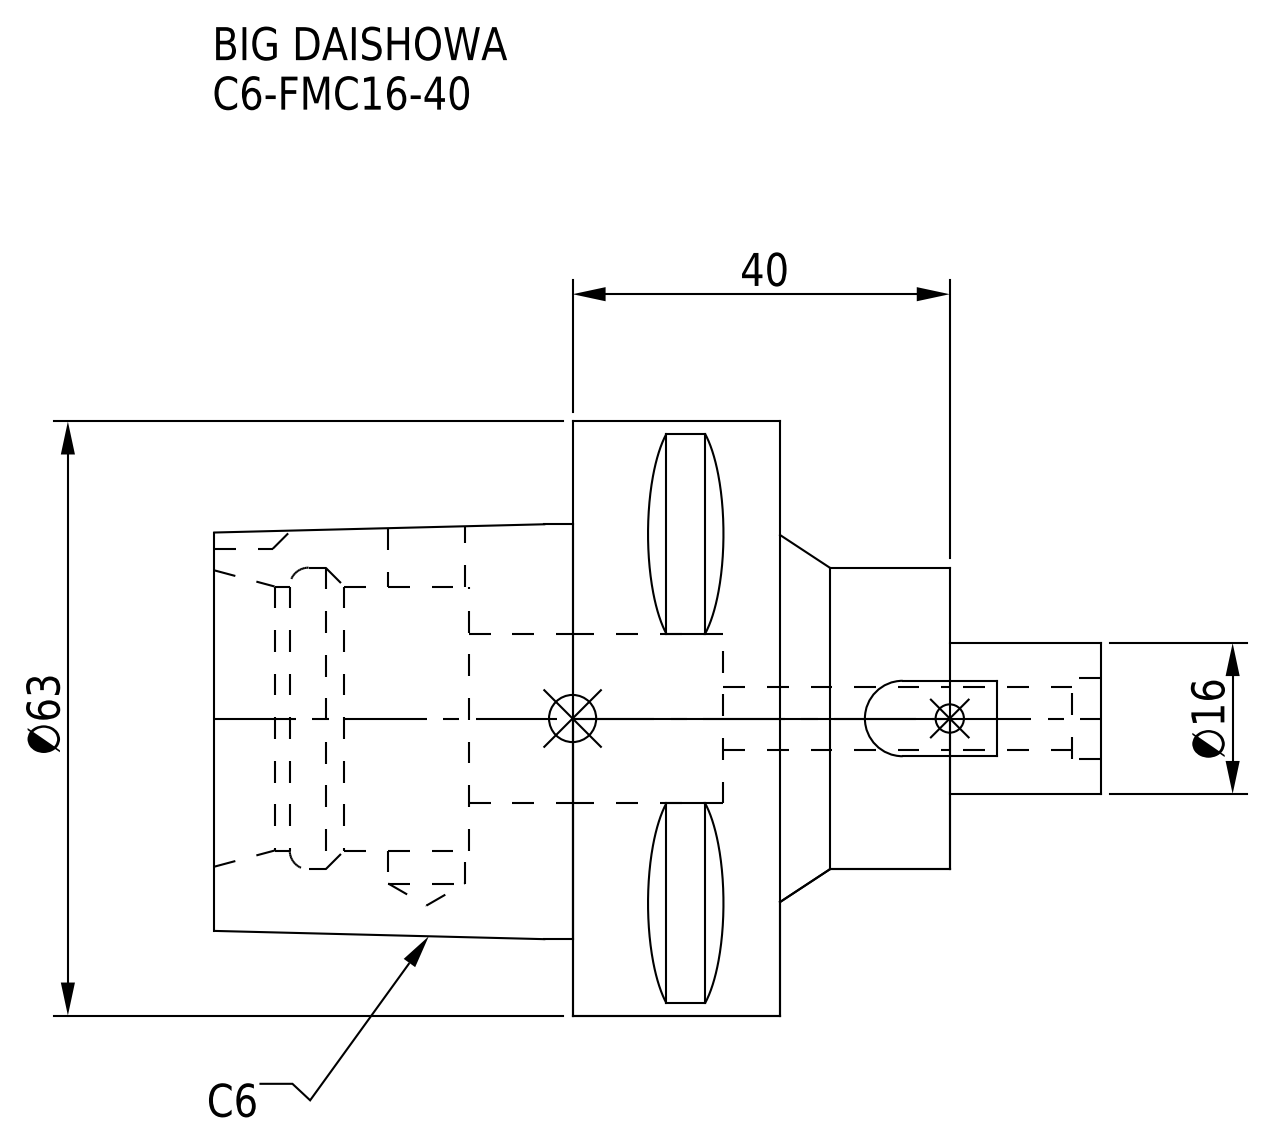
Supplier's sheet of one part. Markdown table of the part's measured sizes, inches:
| quantity | value |
| --- | --- |
| part name | C6-FMC16-40 |
| STEP written by | CREO PARAMETRIC BY PTC INC, 2016380 (AUTOMOTIVE_DESIGN) |
| units | inches |
| bodies | 1 solid, 75 faces (40 planar, 23 cylindrical, 12 other) |
| overall size | 3.701 × 2.48 × 2.48 |
| volume | 6.977 in³ |
| surface area | 36.65 in² |
| round holes (diameter × count) | 0.266 × 1, 0.319 × 1, 0.335 × 1, 0.709 × 1, 1.102 × 1, 1.26 × 1 |
| round bosses / shafts (diameter × count) | 2.48 × 1, 0.63 × 1 |
| partial cylindrical surfaces (radius × count) | 0.197 × 1 |
| main face-to-face distances | 0.866, 1.575, 1.063, 2.362, 1.496, 0.709, 3.071, 0.433, 0.63, 2.008 |
